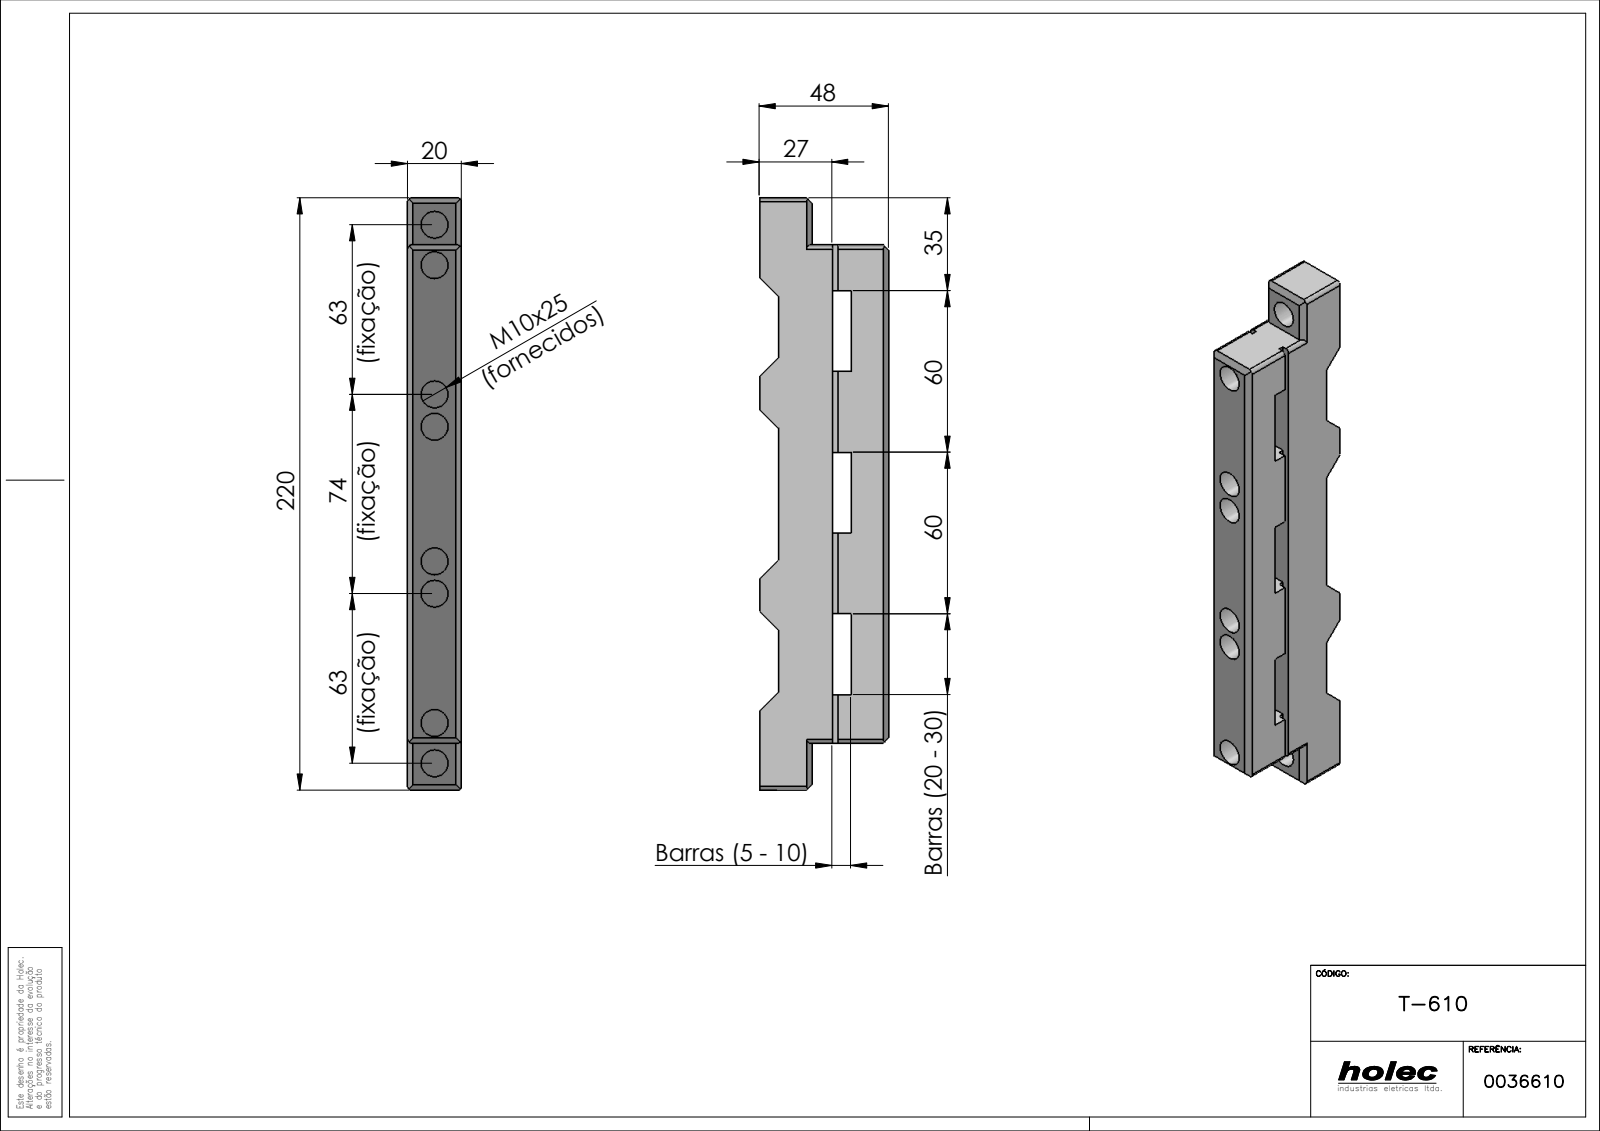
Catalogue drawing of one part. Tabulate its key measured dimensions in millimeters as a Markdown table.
| quantity | value |
| --- | --- |
| part name | T-610 |
| STEP written by | SolidWorks 2017 (AUTOMOTIVE_DESIGN) |
| units | millimeters |
| bodies | 1 solid, 96 faces (68 planar, 28 cylindrical, 0 other) |
| overall size | 220 × 48 × 20 |
| volume | 153 491 mm³ |
| surface area | 34 729 mm² |
| round holes (diameter × count) | 10 × 8 |
| partial cylindrical surfaces (radius × count) | 1.5 × 8 |
| main face-to-face distances | 20, 7, 27, 21, 41, 14, 48, 34, 30, 17.5 |
| hole center spacings | 12, 15, 48, 60, 62, 63, 75, 110 |
